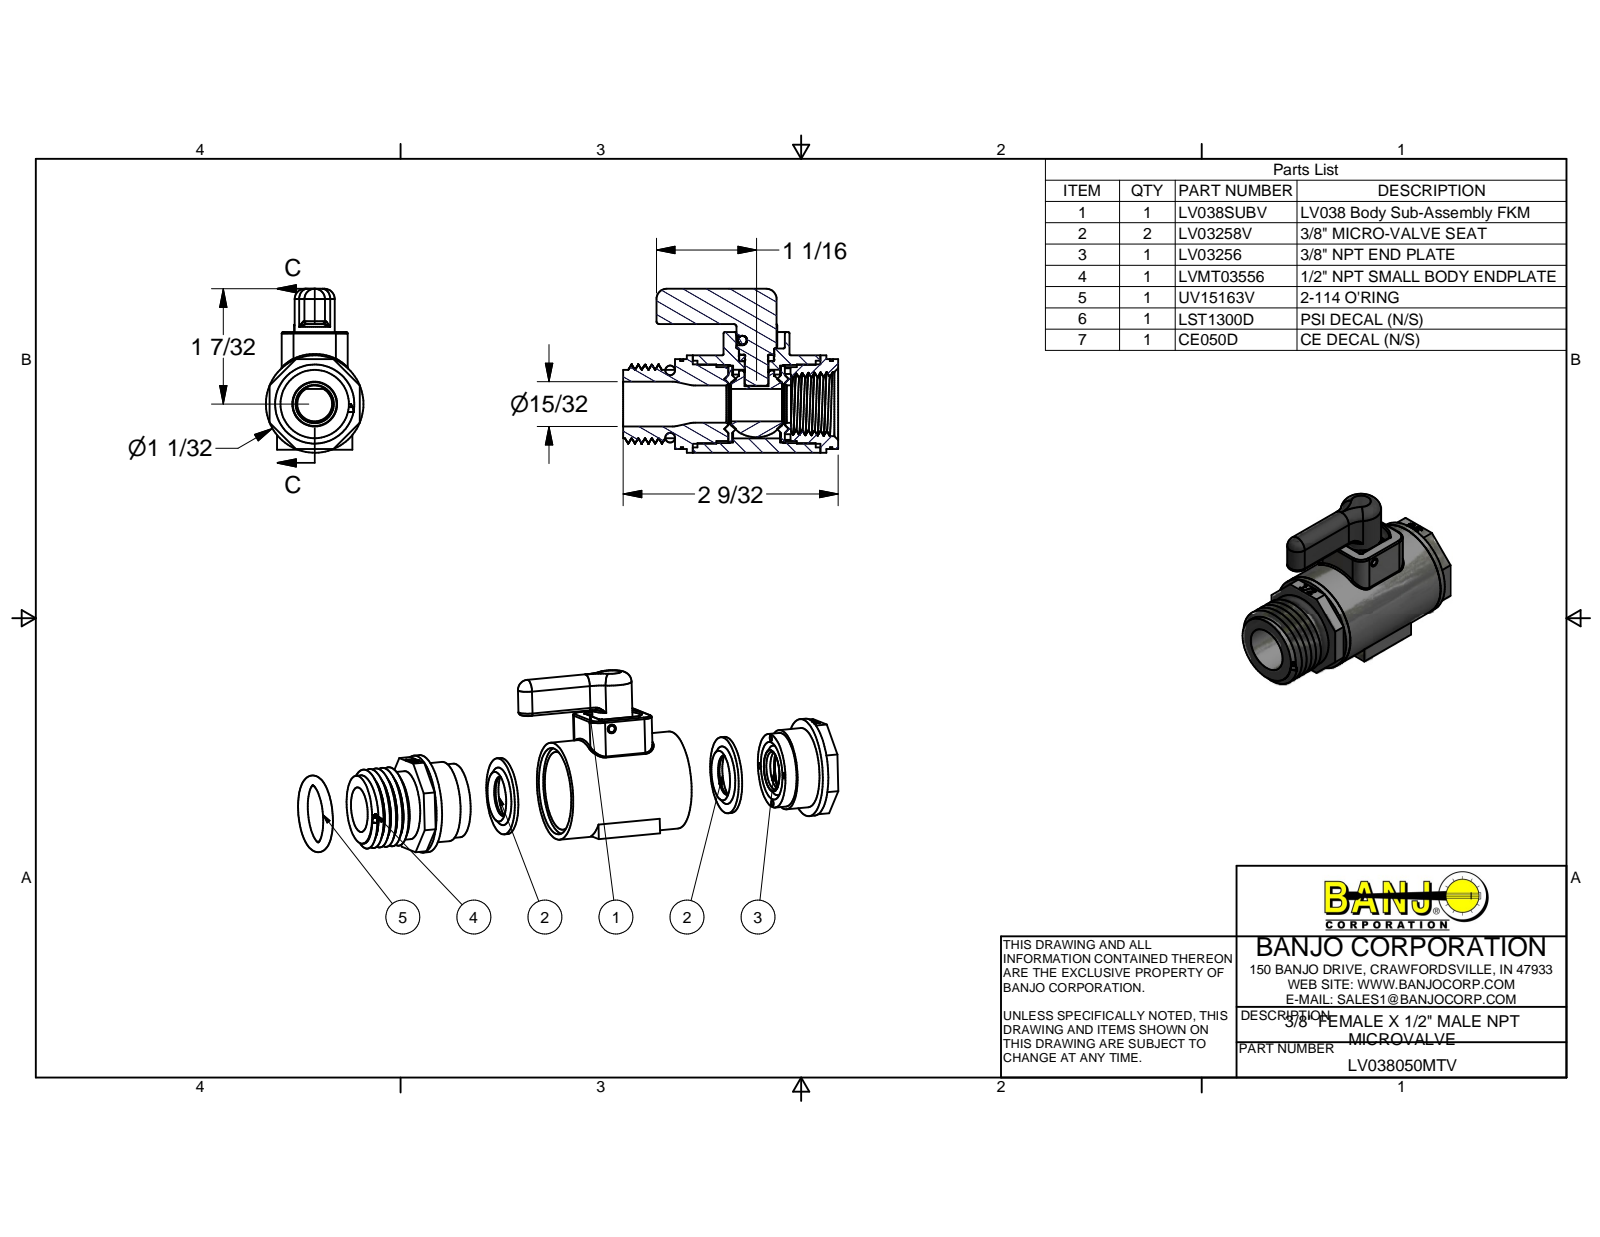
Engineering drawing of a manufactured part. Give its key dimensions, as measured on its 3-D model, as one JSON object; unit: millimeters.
{"part_name": "LV038050MTV; LV038SUBV; LV03254A; AQ010V (+7 more)", "step_written_by": "Autodesk Inventor 2012 (AUTOMOTIVE_DESIGN)", "units": "millimeters", "bodies": {"solids": 9, "faces": 691, "planar": 283, "cylindrical": 111, "other": 297}, "overall_size": [57.9, 44.3, 26.3], "volume_mm3": 17780, "surface_area_mm2": 19060, "round_holes": [[1.5, 4], [2.4, 1], [6.4, 1], [9.3, 1], [9.4, 1], [9.6, 1], [10, 1], [10.2, 1], [10.7, 1], [12.1, 1], [18.5, 1], [20.7, 1]], "round_bosses_or_shafts": [[26.3, 1], [21.5, 1], [20.6, 1], [19.9, 1], [18.4, 1], [10.8, 1], [9.5, 1], [9.4, 1]], "partial_cylinders_radius": [[0.3, 16], [0.4, 14], [3.2, 4], [0.8, 2], [1.3, 2], [2.8, 2], [6.4, 2], [1.2, 1]], "face_to_face_distances": [24.8, 9.6, 1.3, 4.8, 14.4, 29.6, 39.2, 8.3, 34.4, 1], "hole_center_spacings": [8.9, 12.5, 17.8]}
